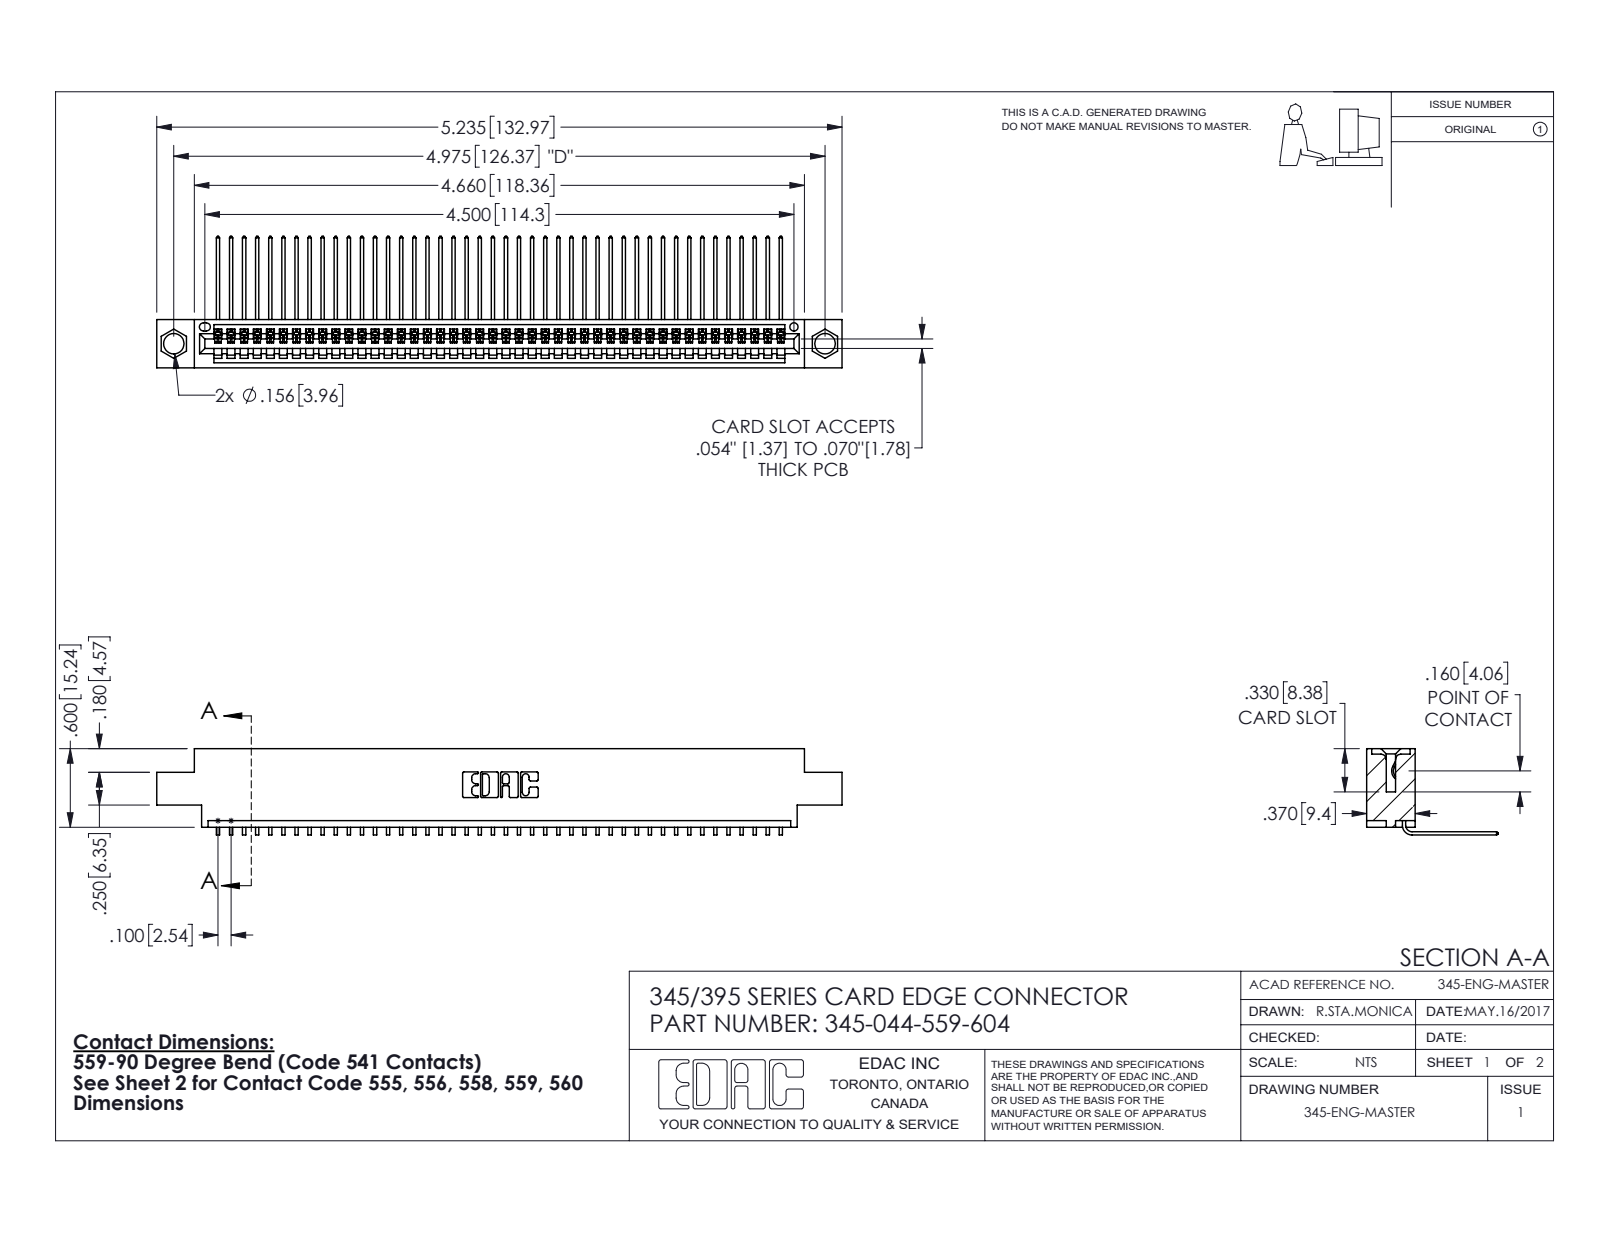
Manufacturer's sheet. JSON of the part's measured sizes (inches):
{"part_name": "345-292-001_558 559 Tail - 1; 345-044-559-604; 345 Part_0.170 Offset - 0.156 Dia-TH", "step_written_by": "SolidWorks 2016 (CONFIG_CONTROL_DESIGN)", "units": "inches", "bodies": {"solids": 45, "faces": 2770, "planar": 1932, "cylindrical": 838, "other": 0}, "overall_size": [5.235, 1.005, 0.659], "volume_in3": 0.768, "surface_area_in2": 27.21, "round_holes": [[0.156, 2], [0.064, 1]], "partial_cylinders_radius": [[0.006, 88], [0.01, 22], [0.007, 6], [0.031, 6], [0.026, 3], [0.031, 2], [0.04, 2], [0.014, 1]], "face_to_face_distances": [0.072, 0.298, 0.37, 0.2, 0.098, 0.272, 0.025, 0.225, 0.175, 0.149], "hole_center_spacings": [0.27, 4.739, 4.975]}
